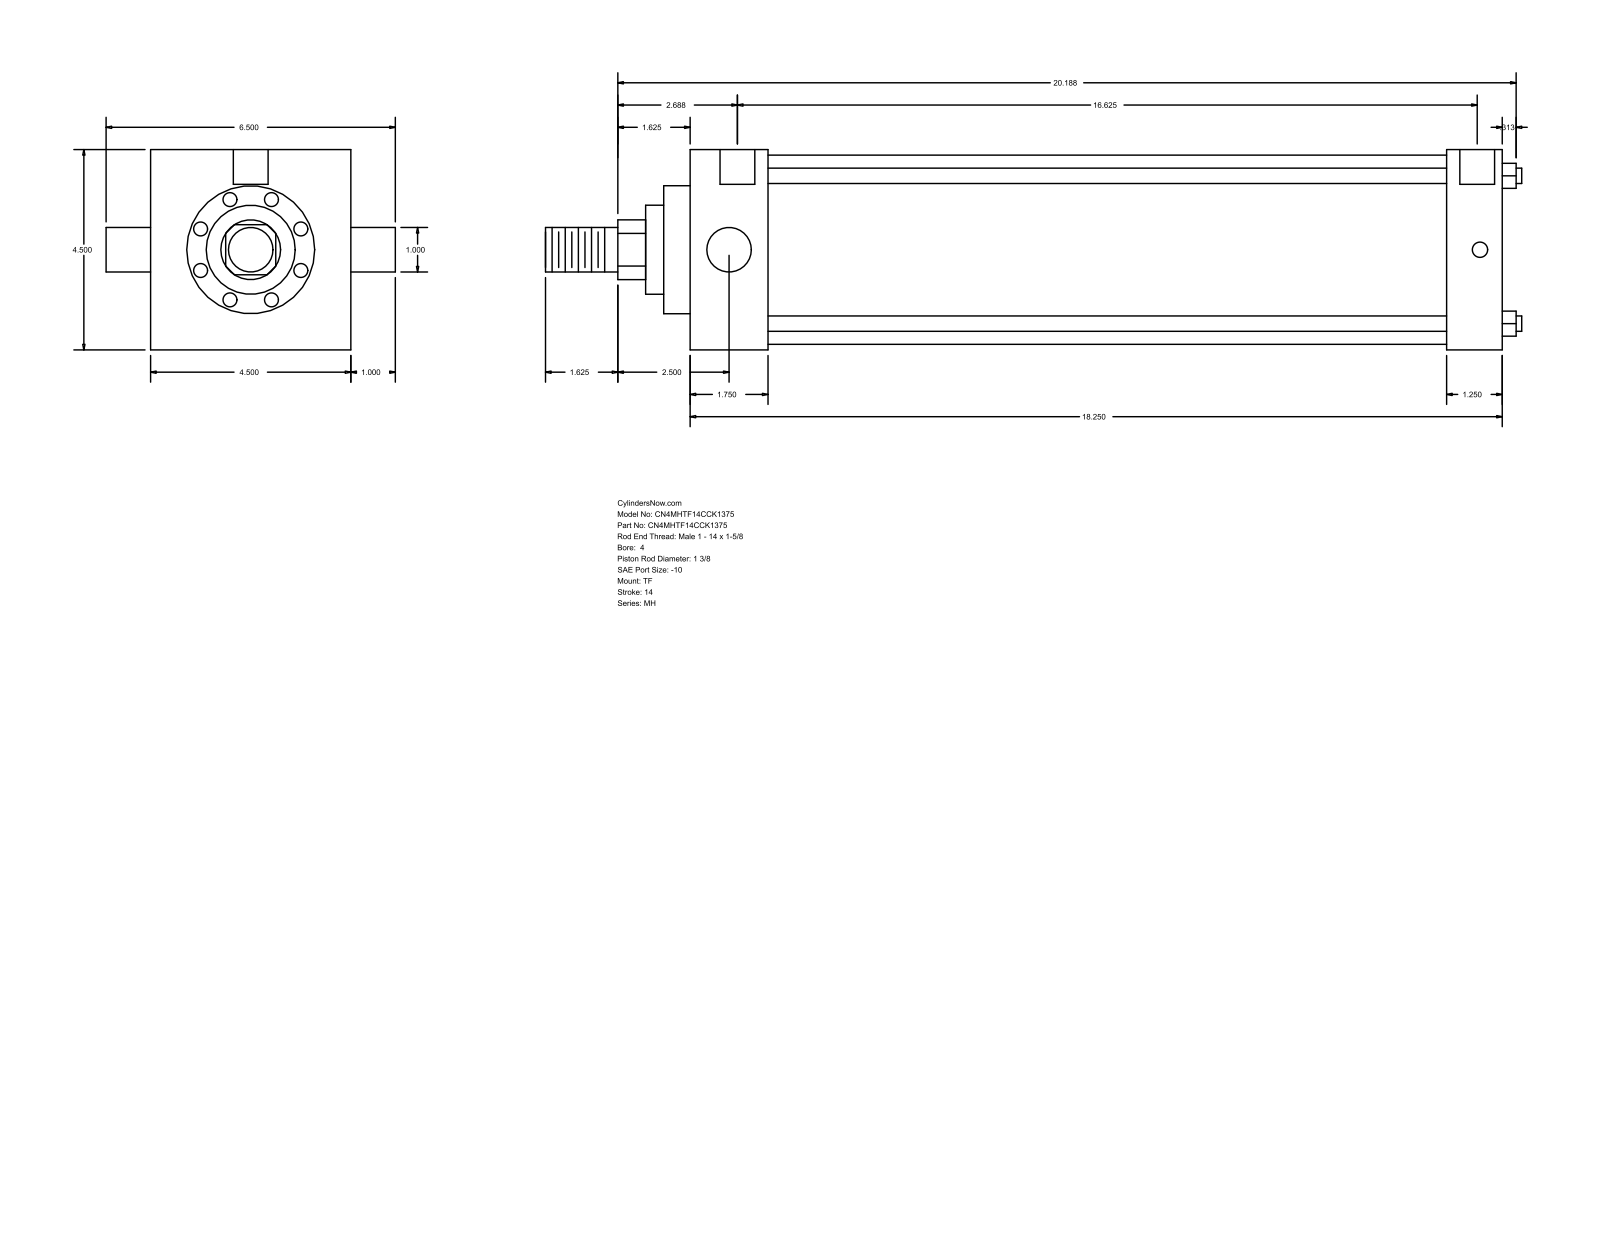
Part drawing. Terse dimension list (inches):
name: MH_TF__0400_1.375
written by: GSSL Pune (CONFIG_CONTROL_DESIGN)
unit: in
bodies: 0 solids, 86 faces (61 planar, 25 cylindrical, 0 other)
size: 21.937 × 6.5 × 4.5
holes: 3× ⌀0.344, 2× ⌀0.781
bosses: 4× ⌀0.345, 2× ⌀1, 1× ⌀4.25, 1× ⌀2.875, 1× ⌀2, 1× ⌀1.375
rounds: 1× R0.672
face distances: 4.5, 18.25, 1.75, 16.5, 17, 15.25, 1.25, 0.594, 2.344, 17.594
hole spacings: 0.062, 0.063, 16.625, 16.687, 16.688, 16.75
